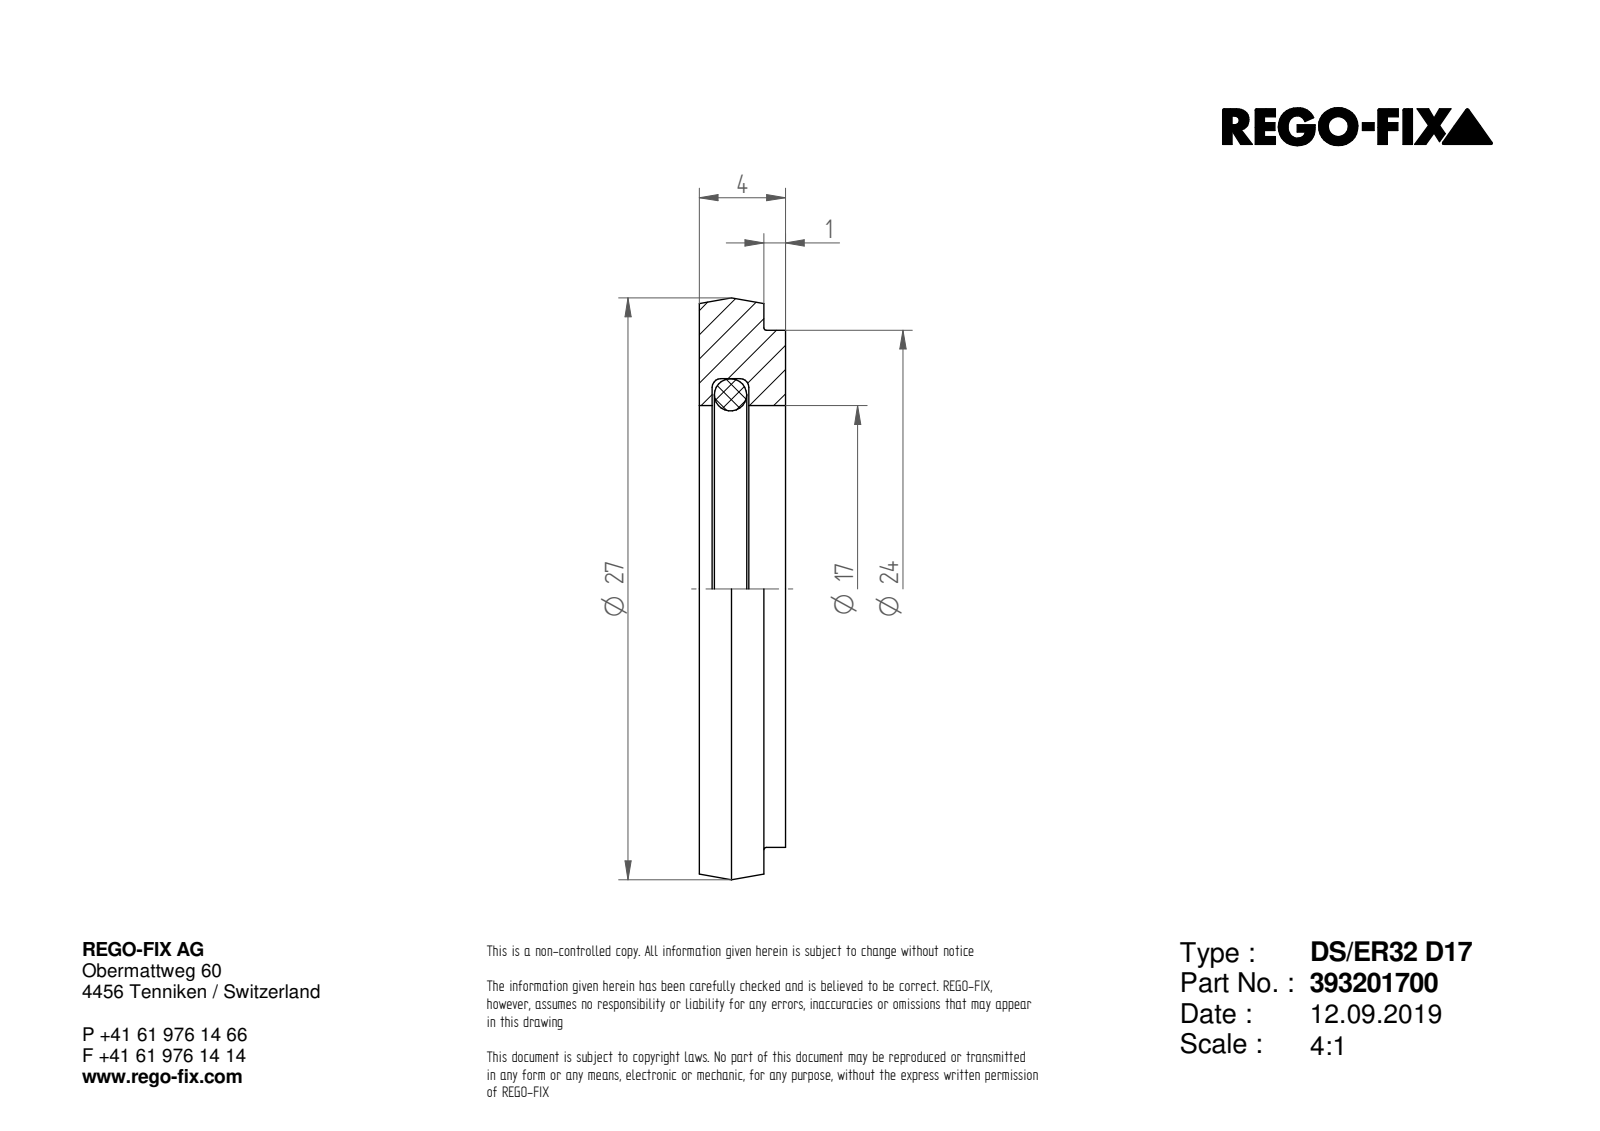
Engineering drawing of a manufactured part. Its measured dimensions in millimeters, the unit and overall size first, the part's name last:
Units: millimetres
Overall size (bounding box): 27 × 27 × 4
Round holes (diameter × count): ⌀17 ×1
Round bosses / shafts (diameter × count): ⌀27 ×1, ⌀24 ×1
Main face-to-face distances: 4, 1, 3
Volume: 1 262 mm³ · Surface area: 1 231 mm²
Bodies: 1 solid, 7 faces (3 planar, 3 cylindrical, 1 other)
Part name (STEP PRODUCT): NOCUT
STEP written by: SIEMENS PLM Software Solid Edge ST10 (AUTOMOTIVE_DESIGN)
